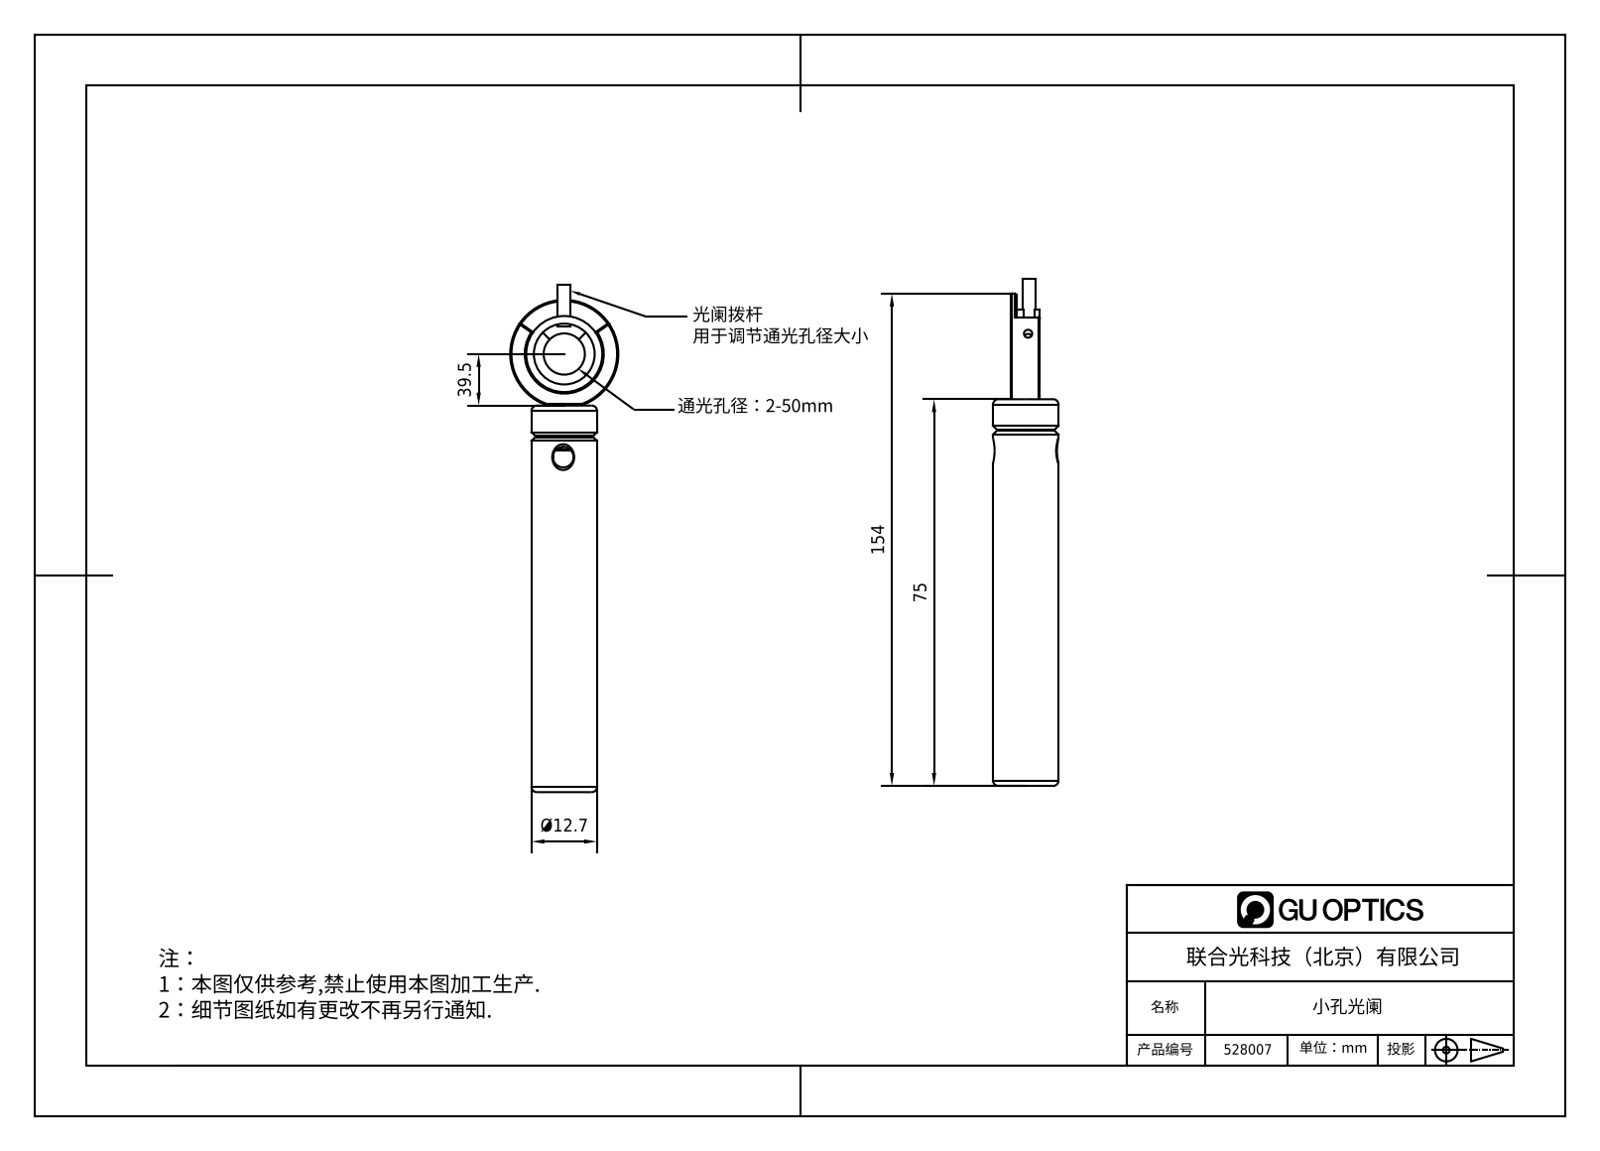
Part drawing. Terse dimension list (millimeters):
name: 528007
written by: SolidWorks 2020 (CONFIG_CONTROL_DESIGN)
unit: mm
bodies: 5 solids, 64 faces (29 planar, 18 cylindrical, 17 other)
size: 158.6 × 79.39 × 12.7
volume: 30 831 mm³; area: 17 124 mm²
holes: 1× ⌀1.25, 1× ⌀3.3, 1× ⌀4, 1× ⌀5, 1× ⌀50, 1× ⌀65.5, 1× ⌀70
bosses: 1× ⌀79.4, 1× ⌀70, 1× ⌀12.7, 1× ⌀4, 1× ⌀2.4, 1× ⌀2, 1× ⌀1.6, 1× ⌀1.4
rounds: 1× R33
face distances: 7.26, 1, 8.26, 8.81, 7.81, 0.55, 1.8, 2.8, 5.46, 6.01
